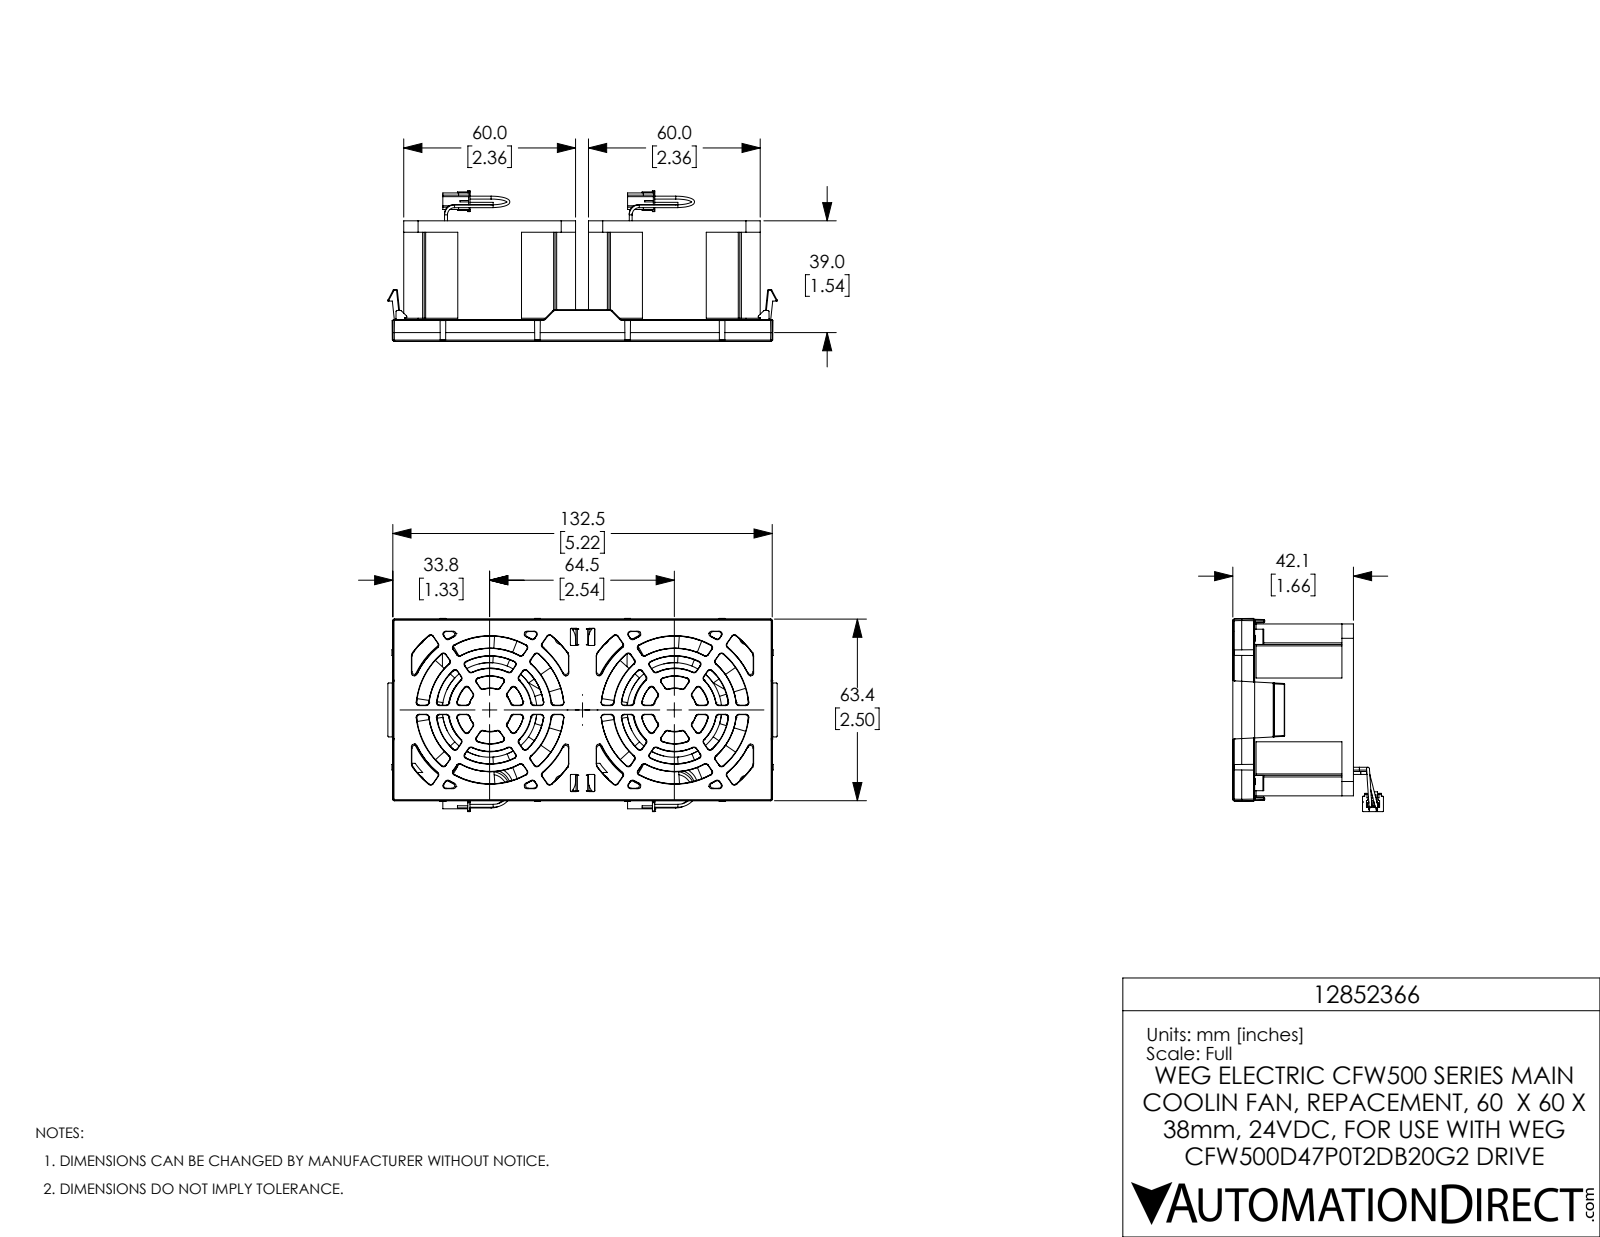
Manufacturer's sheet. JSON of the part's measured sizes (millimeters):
{"part_name": "10002564002swa000 with ext3 Grill COMPLETE 1", "step_written_by": "SolidWorks 2017 (AUTOMOTIVE_DESIGN)", "units": "millimeters", "bodies": {"solids": 15, "faces": 3641, "planar": 1334, "cylindrical": 671, "other": 1636}, "overall_size": [135.9, 67.5, 52.6], "volume_mm3": 139800, "surface_area_mm2": 85290, "round_holes": [[4.3, 8], [57.5, 2]], "round_bosses_or_shafts": [[1, 8], [33, 2]], "partial_cylinders_radius": [[0.3, 133], [0.5, 32], [0.1, 16], [16.5, 14], [28.5, 14], [1, 12], [0.4, 10], [5, 8]], "face_to_face_distances": [60, 19, 3.5, 38.6, 42.1, 0.5, 4.1, 38, 0.6, 64.5], "hole_center_spacings": [35.4, 50, 64.5, 46.8, 70.7, 81.6, 92.9, 14.5]}
